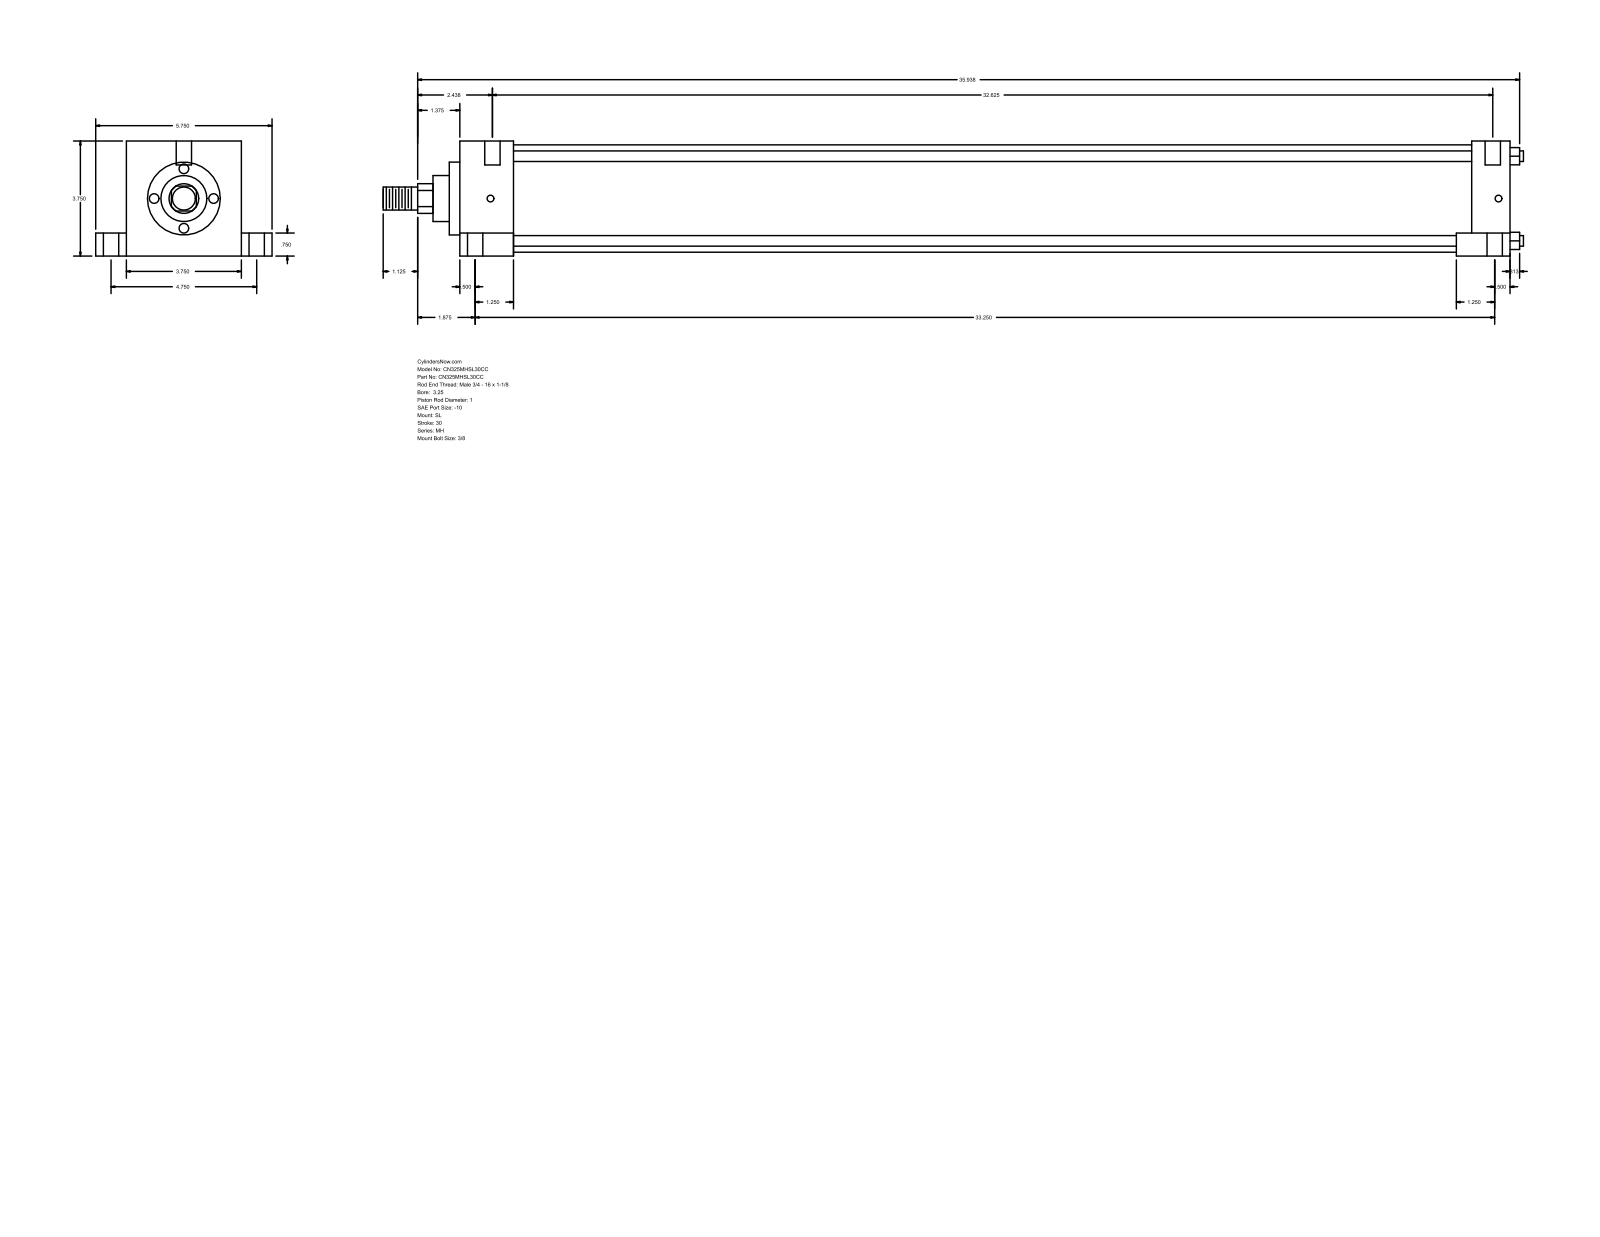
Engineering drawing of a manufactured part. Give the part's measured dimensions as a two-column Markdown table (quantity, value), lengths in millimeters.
| quantity | value |
| --- | --- |
| part name | MH_SL__0325_1 |
| STEP written by | GSSL Pune (CONFIG_CONTROL_DESIGN) |
| units | millimeters |
| bodies | 0 solids, 110 faces (77 planar, 33 cylindrical, 0 other) |
| overall size | 944.56 × 146.05 × 95.25 |
| round holes (diameter × count) | 12.7 × 6, 5.56 × 4, 19.05 × 4 |
| round bosses / shafts (diameter × count) | 8.76 × 4, 88.9 × 1, 60.33 × 1, 38.1 × 1, 25.4 × 1, 19.05 × 1 |
| partial cylindrical surfaces (radius × count) | 12.29 × 1 |
| main face-to-face distances | 95.24, 869.96, 44.46, 825.5, 25.41, 120.65, 19.05, 76.19, 838.2, 793.74 |
| hole center spacings | 60.35, 60.41, 61.65, 62, 120.66, 832.45, 834.02, 835.02 |
